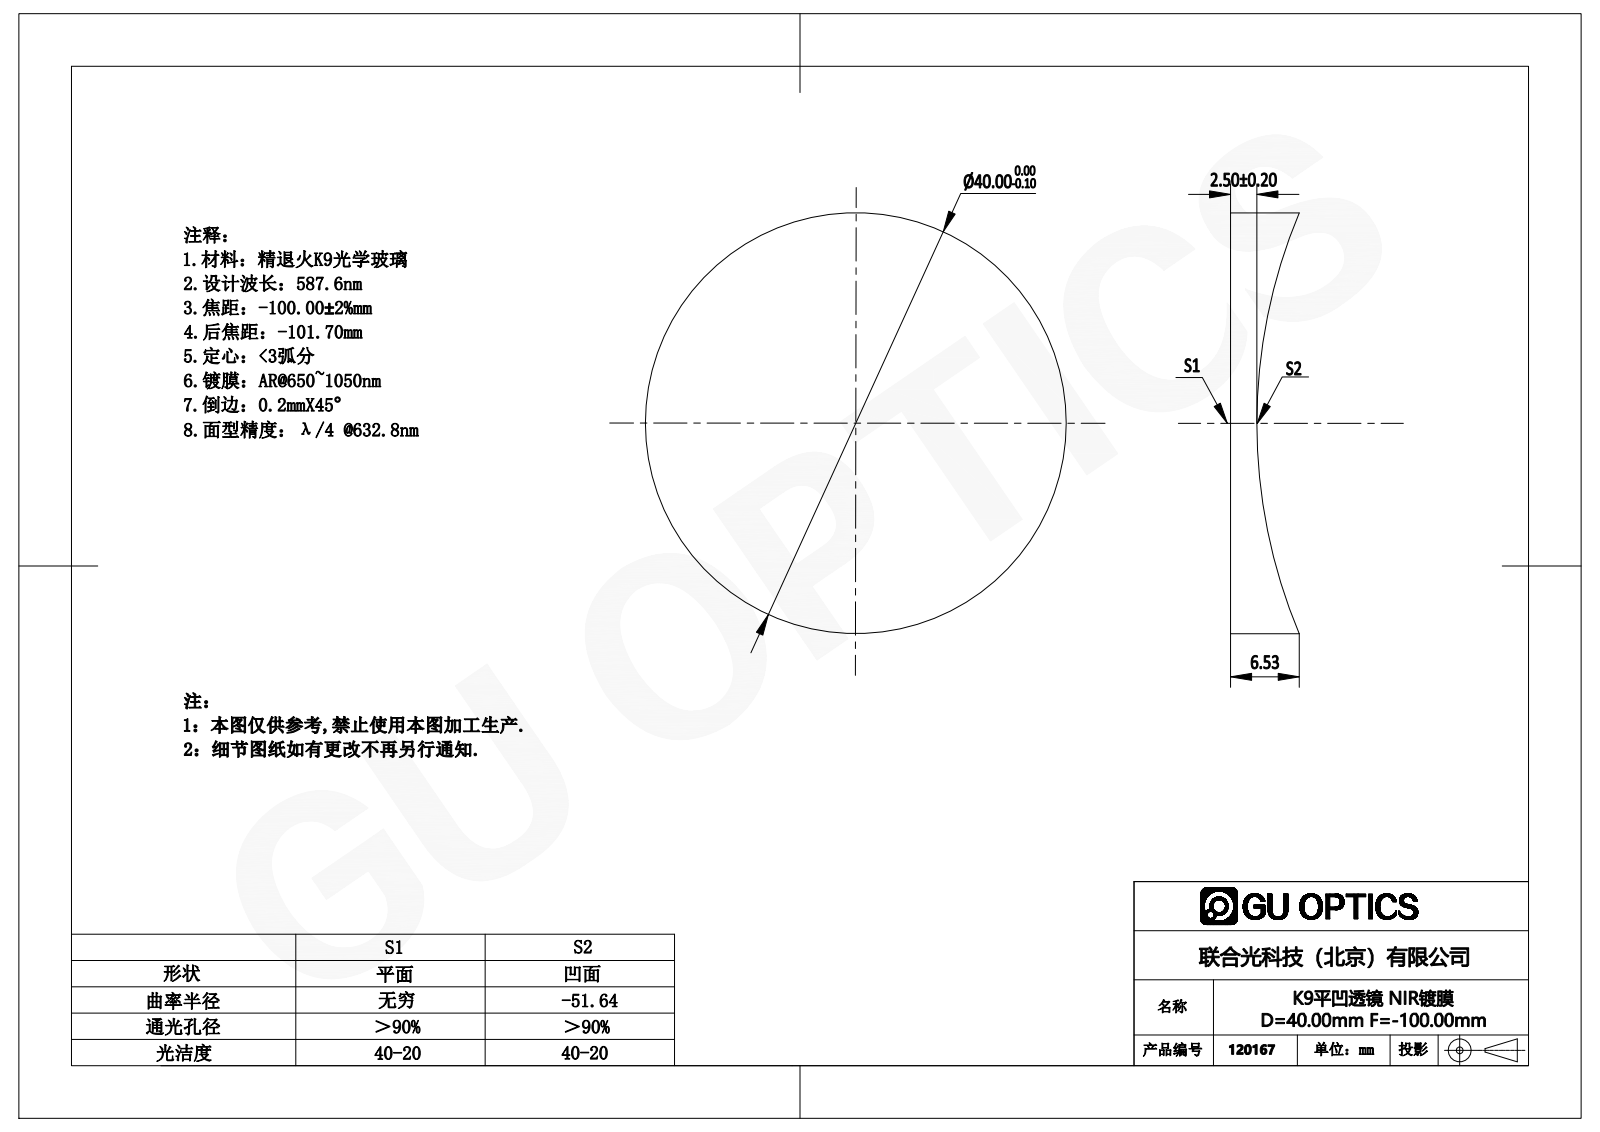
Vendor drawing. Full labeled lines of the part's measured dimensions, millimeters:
Part name (STEP PRODUCT): 120167
STEP written by: SolidWorks 2016 (AUTOMOTIVE_DESIGN)
Units: millimetres
Bodies: 1 solid, 5 faces (1 planar, 2 cylindrical, 2 other)
Overall size (bounding box): 40 × 40 × 6.53
Volume: 5 640 mm³ · Surface area: 3 385 mm²
Round bosses / shafts (diameter × count): ⌀40 ×1
